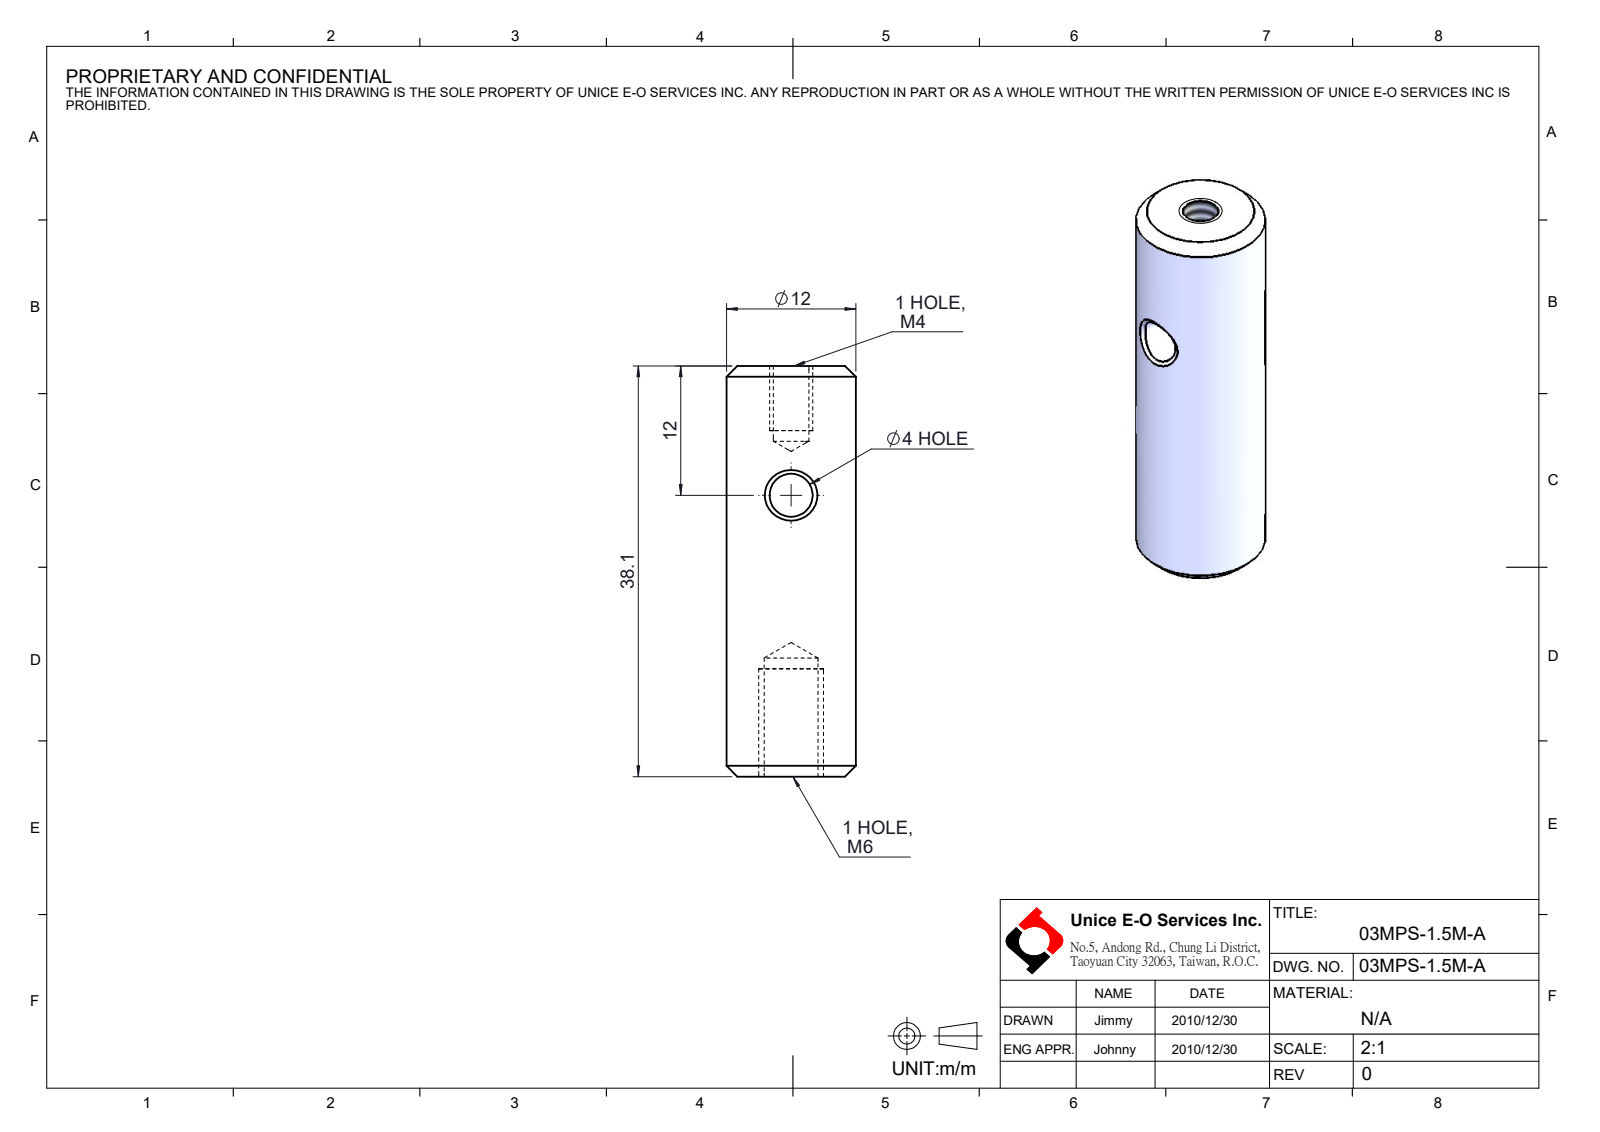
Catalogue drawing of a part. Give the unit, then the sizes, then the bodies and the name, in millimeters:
Units: millimetres
Overall size (bounding box): 38.1 × 12 × 12
Round holes (diameter × count): ⌀3.3 ×1, ⌀4 ×1, ⌀5 ×1
Round bosses / shafts (diameter × count): ⌀12 ×1
Main face-to-face distances: 38.1
Volume: 3 835 mm³ · Surface area: 1 980 mm²
Bodies: 1 solid, 22 faces (2 planar, 8 cylindrical, 12 other)
Part name (STEP PRODUCT): 03MPS-1.5M-A
STEP written by: SolidWorks 2016 (CONFIG_CONTROL_DESIGN)
